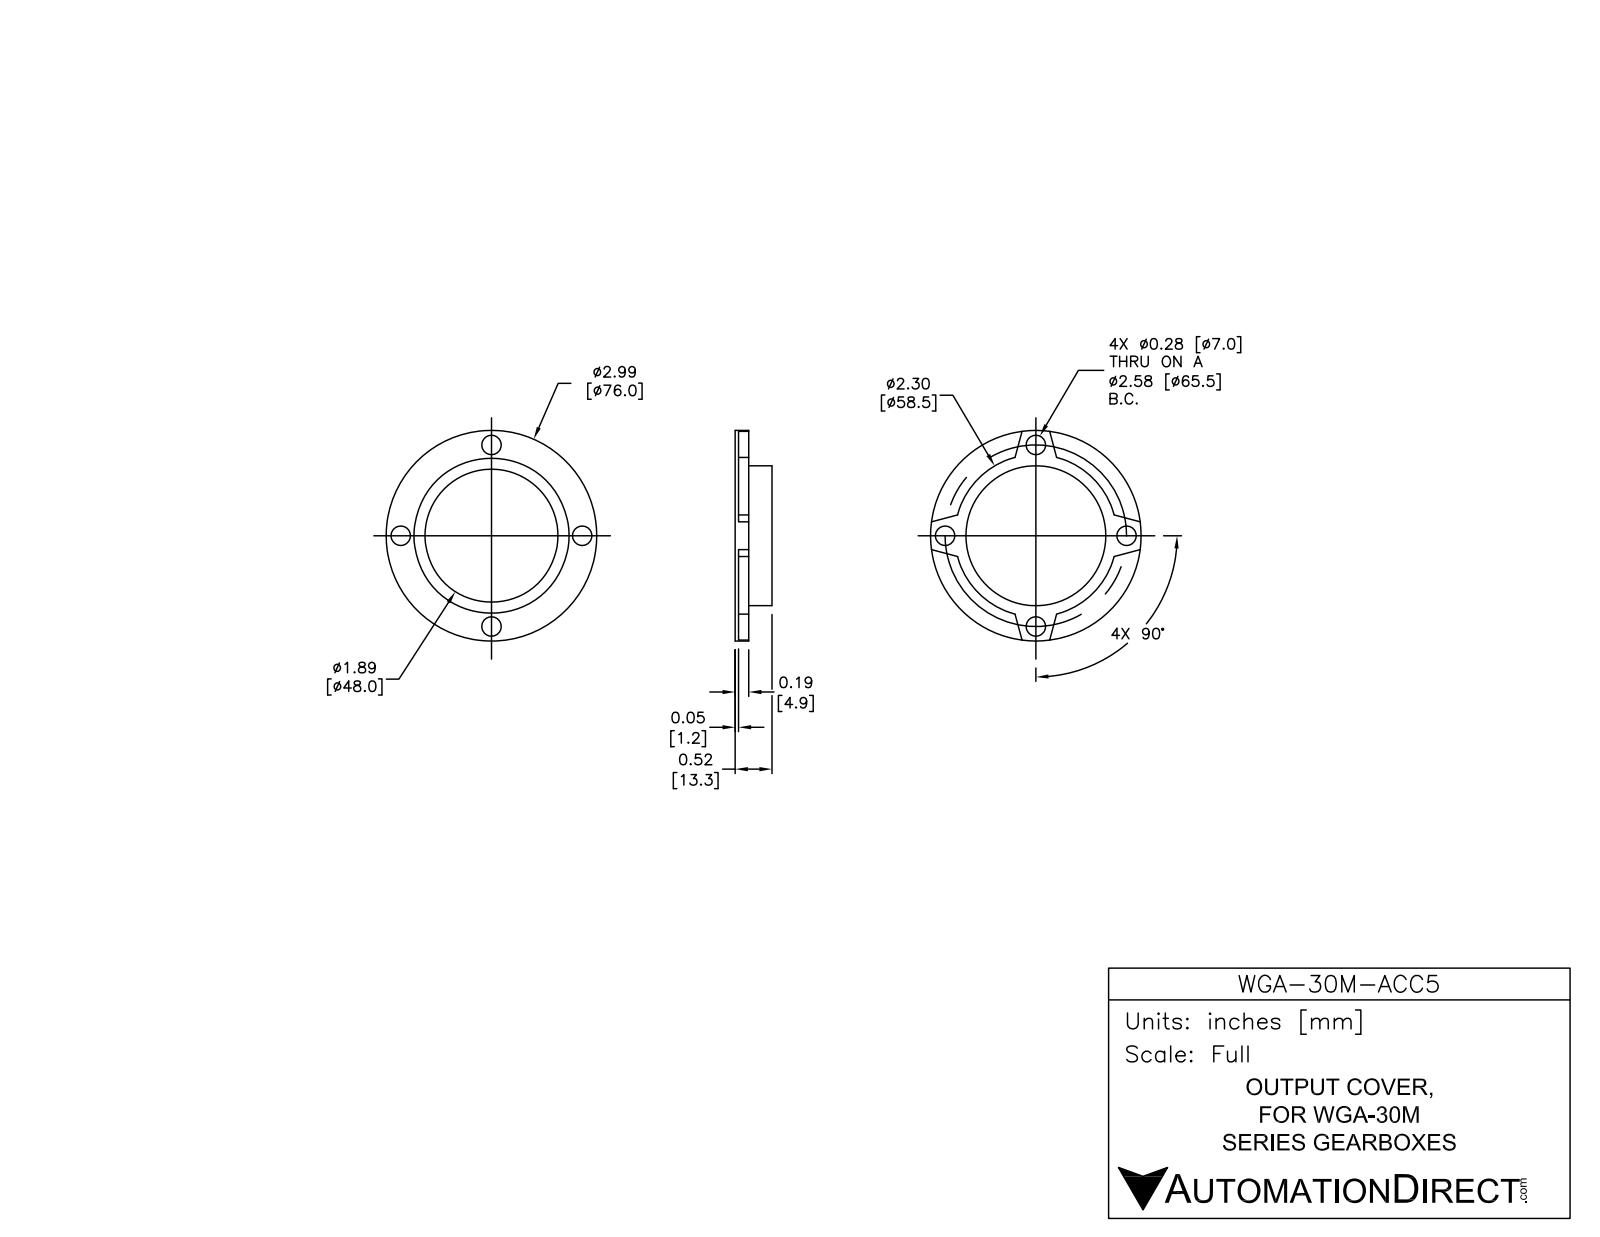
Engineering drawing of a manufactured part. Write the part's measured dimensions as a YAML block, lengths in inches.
part_name: "WGA-30M-ACC5"
step_written_by: "SolidWorks 2014 (AUTOMOTIVE_DESIGN)"
units: inches
bodies: {solids: 1, faces: 37, planar: 17, cylindrical: 20, other: 0}
overall_size: [2.992, 2.992, 0.524]
volume: 0.613
surface_area: 20.95
round_holes:
  - {diameter: 0.276, count: 4}
  - {diameter: 1.89, count: 1}
  - {diameter: 2.205, count: 1}
round_bosses_or_shafts:
  - {diameter: 2.992, count: 1}
  - {diameter: 1.988, count: 1}
partial_cylinders:
  - {radius: 1.152, count: 1}
face_to_face_distances: [0.047, 0.524, 0.075, 0.449, 0.146, 0.476, 0.402, 0.331, 0.256, 0.193]
hole_center_spacings: [1.289, 1.824, 2.579]
